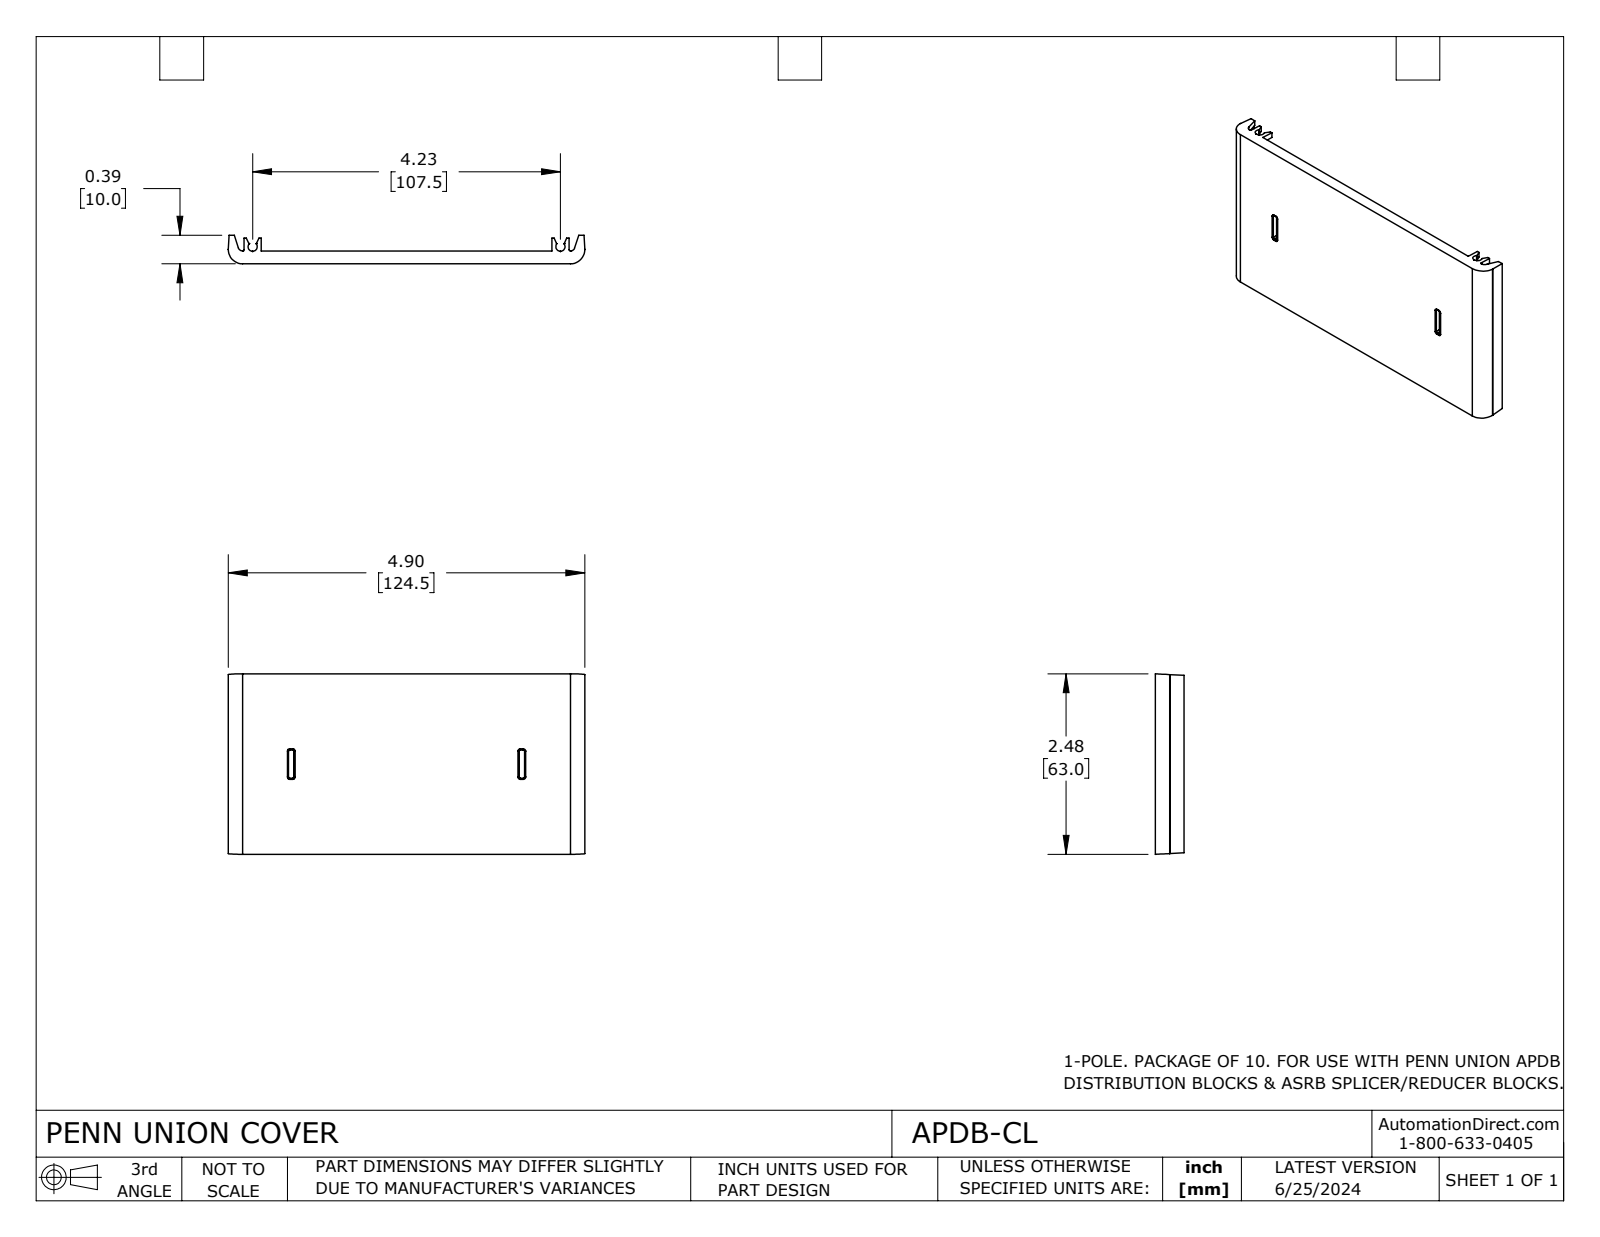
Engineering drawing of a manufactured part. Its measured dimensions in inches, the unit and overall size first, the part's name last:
Units: inches
Overall size (bounding box): 4.902 × 2.48 × 0.394
Partial cylindrical surfaces — rounded edges, fillets, slot ends (radius × count): R0.02 ×10, R0.012 ×6, R0.059 ×2, R0.063 ×2, R0.126 ×2, R0.197 ×2
Main face-to-face distances: 0.071, 0.177, 0.106, 0.217, 0.323, 0.394, 4.232, 0.236, 3.169, 3.996
Volume: 1.038 in³ · Surface area: 30.16 in²
Bodies: 1 solid, 120 faces (72 planar, 36 cylindrical, 12 other)
Part name (STEP PRODUCT): APDB-CL
STEP written by: SolidWorks 2023 (CONFIG_CONTROL_DESIGN)
